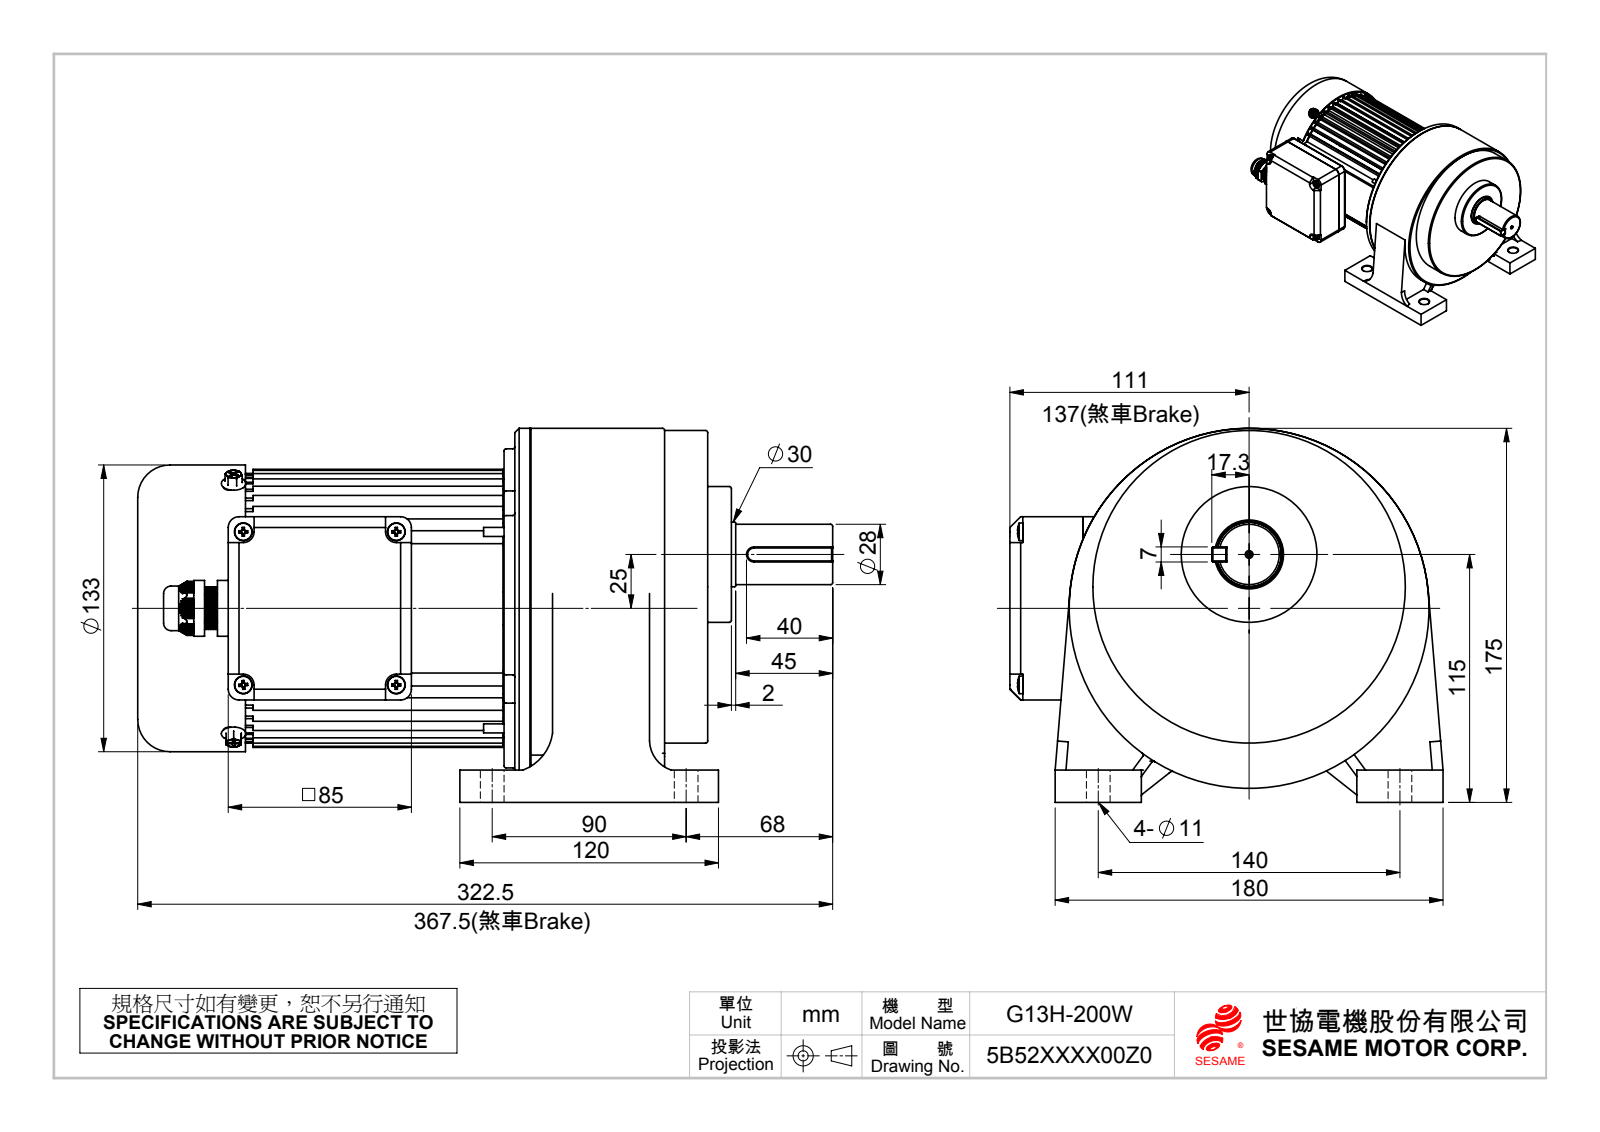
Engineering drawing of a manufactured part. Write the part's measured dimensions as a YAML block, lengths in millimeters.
part_name: "M100CD1-45; 出線盒墊片JTH-UP3(PVC2mm厚); 油封30x55x8; G13HBOX1_Z-成品 (+8 more)"
step_written_by: "SolidWorks 2010 (CONFIG_CONTROL_DESIGN)"
units: millimeters
bodies: {solids: 19, faces: 2841, planar: 855, cylindrical: 913, other: 1073}
overall_size: [322.5, 201, 173.5]
volume: 4129000
surface_area: 524086
round_holes:
  - {diameter: 5, count: 11}
  - {diameter: 3.3, count: 9}
  - {diameter: 8, count: 9}
  - {diameter: 5.1, count: 5}
  - {diameter: 11, count: 4}
  - {diameter: 4.2, count: 3}
  - {diameter: 2, count: 1}
  - {diameter: 7.5, count: 1}
  - {diameter: 10.8, count: 1}
  - {diameter: 16.5, count: 1}
  - {diameter: 30, count: 1}
  - {diameter: 31, count: 1}
round_bosses_or_shafts:
  - {diameter: 8.3, count: 4}
  - {diameter: 4.2, count: 4}
  - {diameter: 4, count: 4}
  - {diameter: 5, count: 3}
  - {diameter: 167, count: 1}
  - {diameter: 148, count: 1}
  - {diameter: 145, count: 1}
  - {diameter: 133, count: 1}
partial_cylinders:
  - {radius: 1, count: 103}
  - {radius: 1.03, count: 8}
  - {radius: 3, count: 8}
  - {radius: 5, count: 8}
  - {radius: 2.75, count: 6}
  - {radius: 8, count: 5}
  - {radius: 2, count: 4}
  - {radius: 2.55, count: 4}
face_to_face_distances: [2, 102, 113, 10, 18, 110, 13, 112, 7.5, 77]
hole_center_spacings: [89.35, 144.57, 45, 71, 76.01, 11, 11.5, 14.6]
